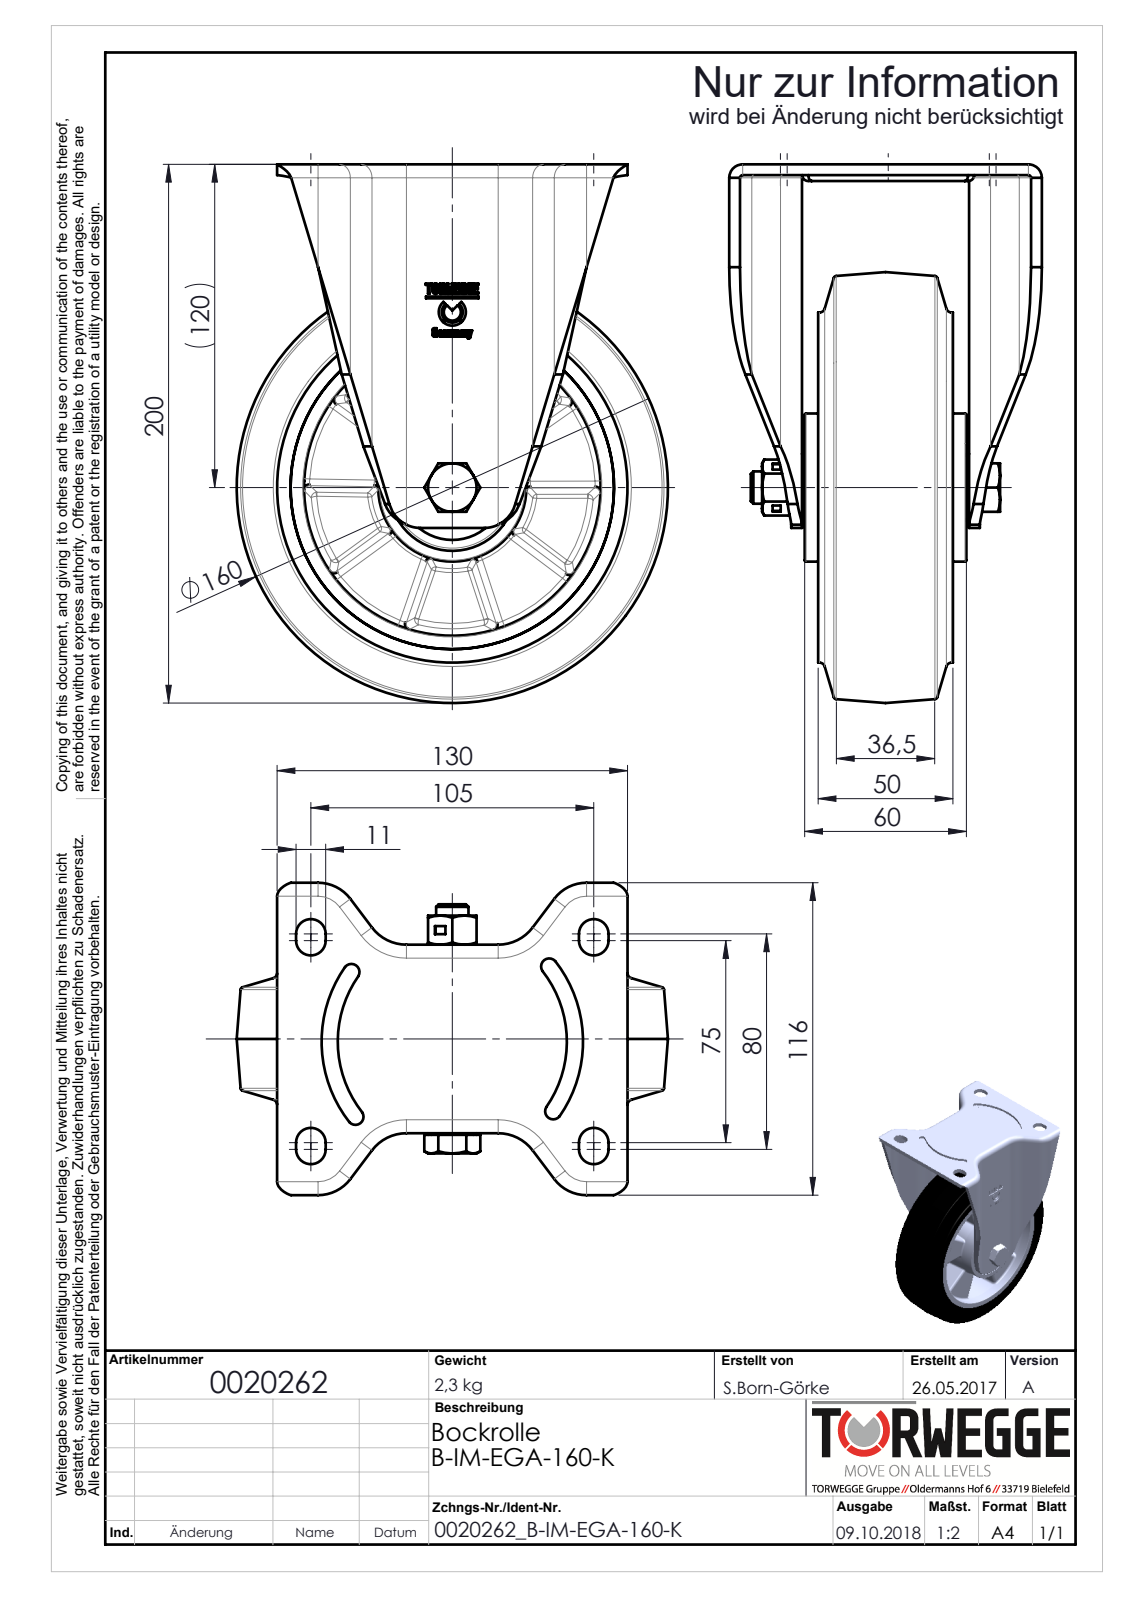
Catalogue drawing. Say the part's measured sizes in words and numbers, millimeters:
The part is named "0020262_B-IM-EGA-160-K". Its 3-D file was written by "SolidWorks 2016 (AUTOMOTIVE_DESIGN)". It is 0 solids with 927 faces: 299 planar, 237 cylindrical and 391 other. Overall it measures 200 by 160 by 116 millimeters. Round holes: 1 of diameter 10.2, 1 of diameter 12, 1 of diameter 12.2, 1 of diameter 20, 1 of diameter 21, 1 of diameter 28.1, 1 of diameter 38, 1 of diameter 38.9, 1 of diameter 47, 1 of diameter 110, 1 of diameter 120. Round bosses or shafts: 1 of diameter 130, 1 of diameter 55, 1 of diameter 25, 1 of diameter 19.9, 1 of diameter 18. Partial cylindrical surfaces (rounded edges, fillets, slot ends): 20 of radius 1.5, 20 of radius 2.5, 8 of radius 0.37, 8 of radius 1, 8 of radius 5, 8 of radius 5.5, 5 of radius 0.62, 4 of radius 0.93. The main face-to-face distances are 4, 66, 60, 47.5, 6, 10, 56, 18.5, 51.5, 14.5.
